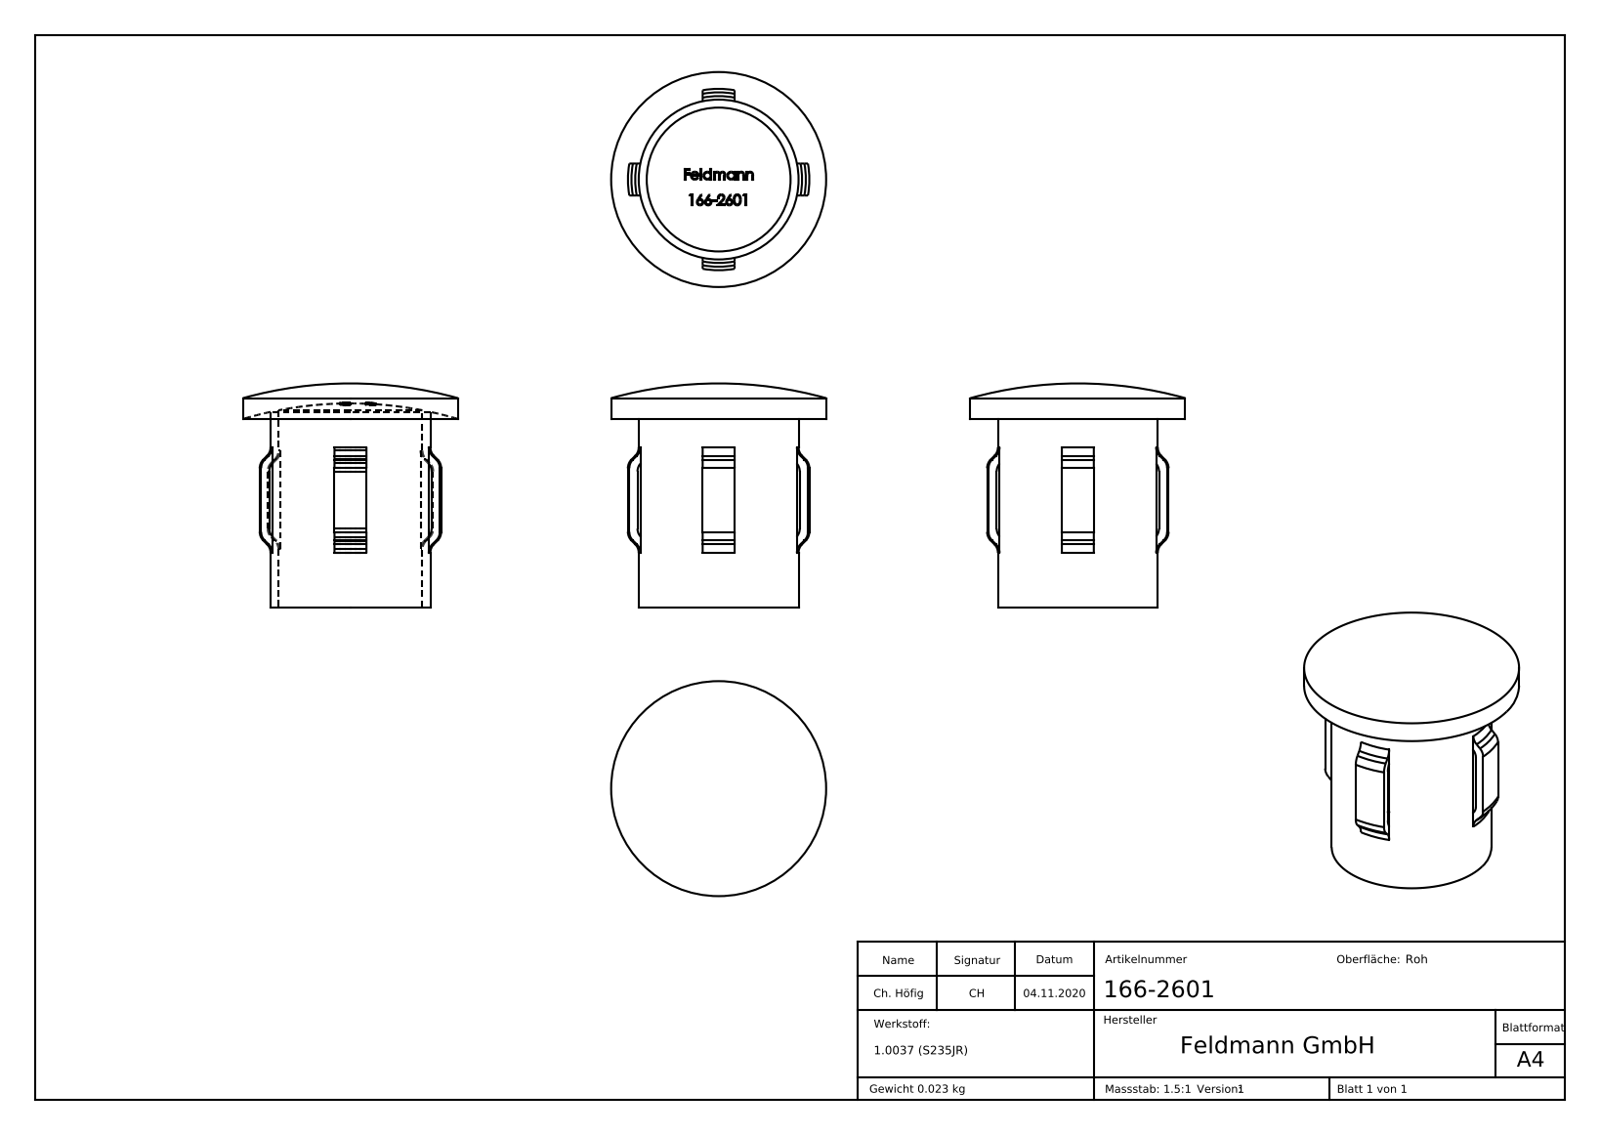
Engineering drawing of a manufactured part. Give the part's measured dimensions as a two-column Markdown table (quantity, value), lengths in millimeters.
| quantity | value |
| --- | --- |
| part name | 166-2601 |
| STEP written by | SolidWorks 2018 (CONFIG_CONTROL_DESIGN) |
| units | millimeters |
| bodies | 1 solid, 306 faces (102 planar, 16 cylindrical, 188 other) |
| overall size | 28 × 26.9 × 26.9 |
| volume | 2 931 mm³ |
| surface area | 4 518 mm² |
| round holes (diameter × count) | 18 × 1 |
| round bosses / shafts (diameter × count) | 26.9 × 1, 20 × 1 |
| partial cylindrical surfaces (radius × count) | 10.35 × 1, 11.35 × 1 |
| main face-to-face distances | 4, 2.97, 2, 0.39, 1.26, 6.72, 3.66, 3.27, 0.87, 7.59 |
